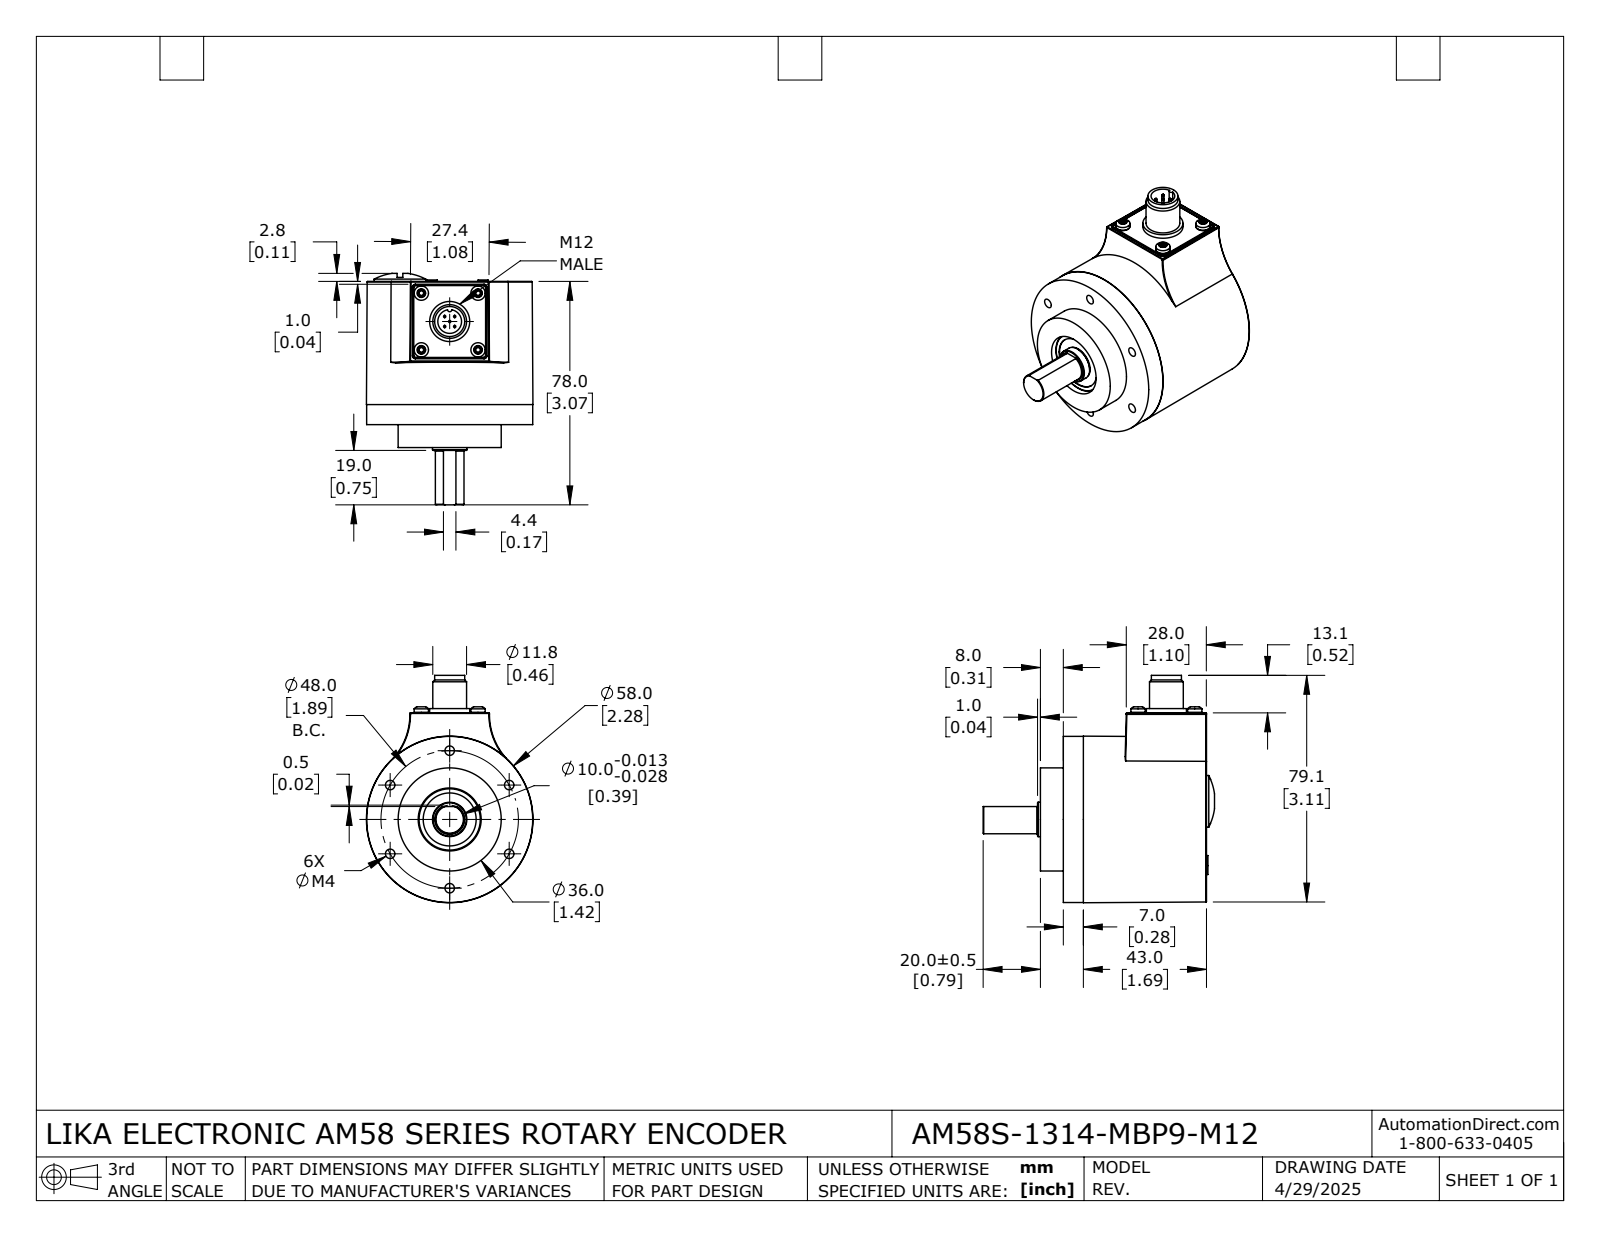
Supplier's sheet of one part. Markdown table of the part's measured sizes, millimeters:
| quantity | value |
| --- | --- |
| part name | AM58S-1314-MBP9-M12 |
| STEP written by | SolidWorks 2024 (AUTOMOTIVE_DESIGN) |
| units | millimeters |
| bodies | 41 solids, 1629 faces (932 planar, 354 cylindrical, 343 other) |
| overall size | 80.8 × 79.4 × 58.1 |
| volume | 59 290 mm³ |
| surface area | 51 300 mm² |
| round holes (diameter × count) | 3.3 × 6, 1.6 × 4, 2.1 × 4, 3.2 × 4, 2.5 × 3, 3.5 × 2, 8 × 2, 8.3 × 1, 10 × 1, 11.7 × 1, 12.5 × 1, 14.5 × 1 |
| round bosses / shafts (diameter × count) | 3 × 5, 1.3 × 5, 0.8 × 5, 5 × 4, 2.5 × 4, 14 × 2, 58 × 1, 55.5 × 1 |
| partial cylindrical surfaces (radius × count) | 0.2 × 24, 0.4 × 24, 0.2 × 19, 0.2 × 9, 0.5 × 6, 3 × 3, 0.8 × 1 |
| main face-to-face distances | 1, 3, 2, 10, 50, 2.5, 7, 8, 47.5, 10.5 |
| hole center spacings | 24, 42, 14, 15, 19.8, 21.2, 24.3, 41.6 |
